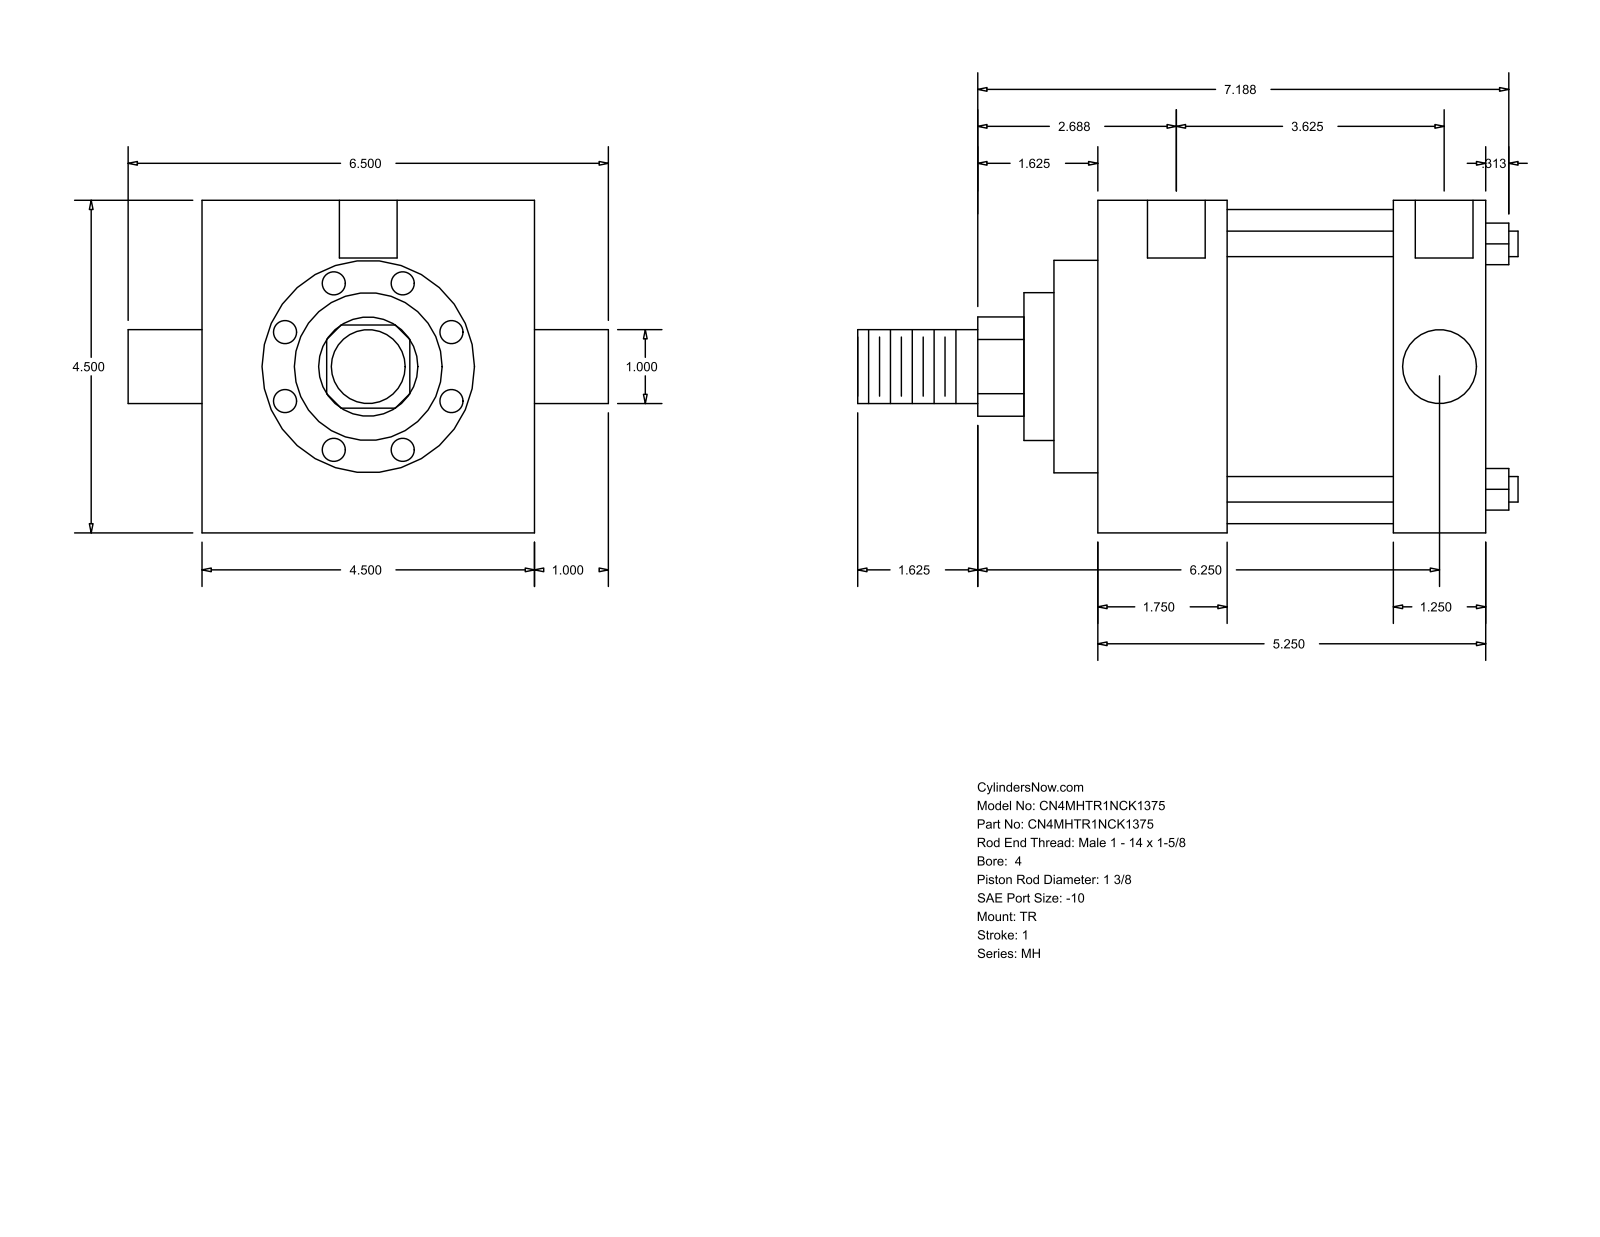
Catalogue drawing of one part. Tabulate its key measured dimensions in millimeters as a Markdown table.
| quantity | value |
| --- | --- |
| part name | MH_TR__0400_1.375 |
| STEP written by | GSSL Pune (CONFIG_CONTROL_DESIGN) |
| units | millimeters |
| bodies | 0 solids, 86 faces (61 planar, 25 cylindrical, 0 other) |
| overall size | 227.01 × 165.1 × 114.3 |
| round holes (diameter × count) | 8.73 × 3, 19.84 × 2 |
| round bosses / shafts (diameter × count) | 8.76 × 4, 25.4 × 2, 107.95 × 1, 73.03 × 1, 50.8 × 1, 34.92 × 1 |
| partial cylindrical surfaces (radius × count) | 17.06 × 1 |
| main face-to-face distances | 114.3, 133.35, 44.45, 88.9, 101.61, 57.16, 31.74, 15.08, 59.53, 116.69 |
| hole center spacings | 1.59, 93.67, 92.08, 95.26 |
